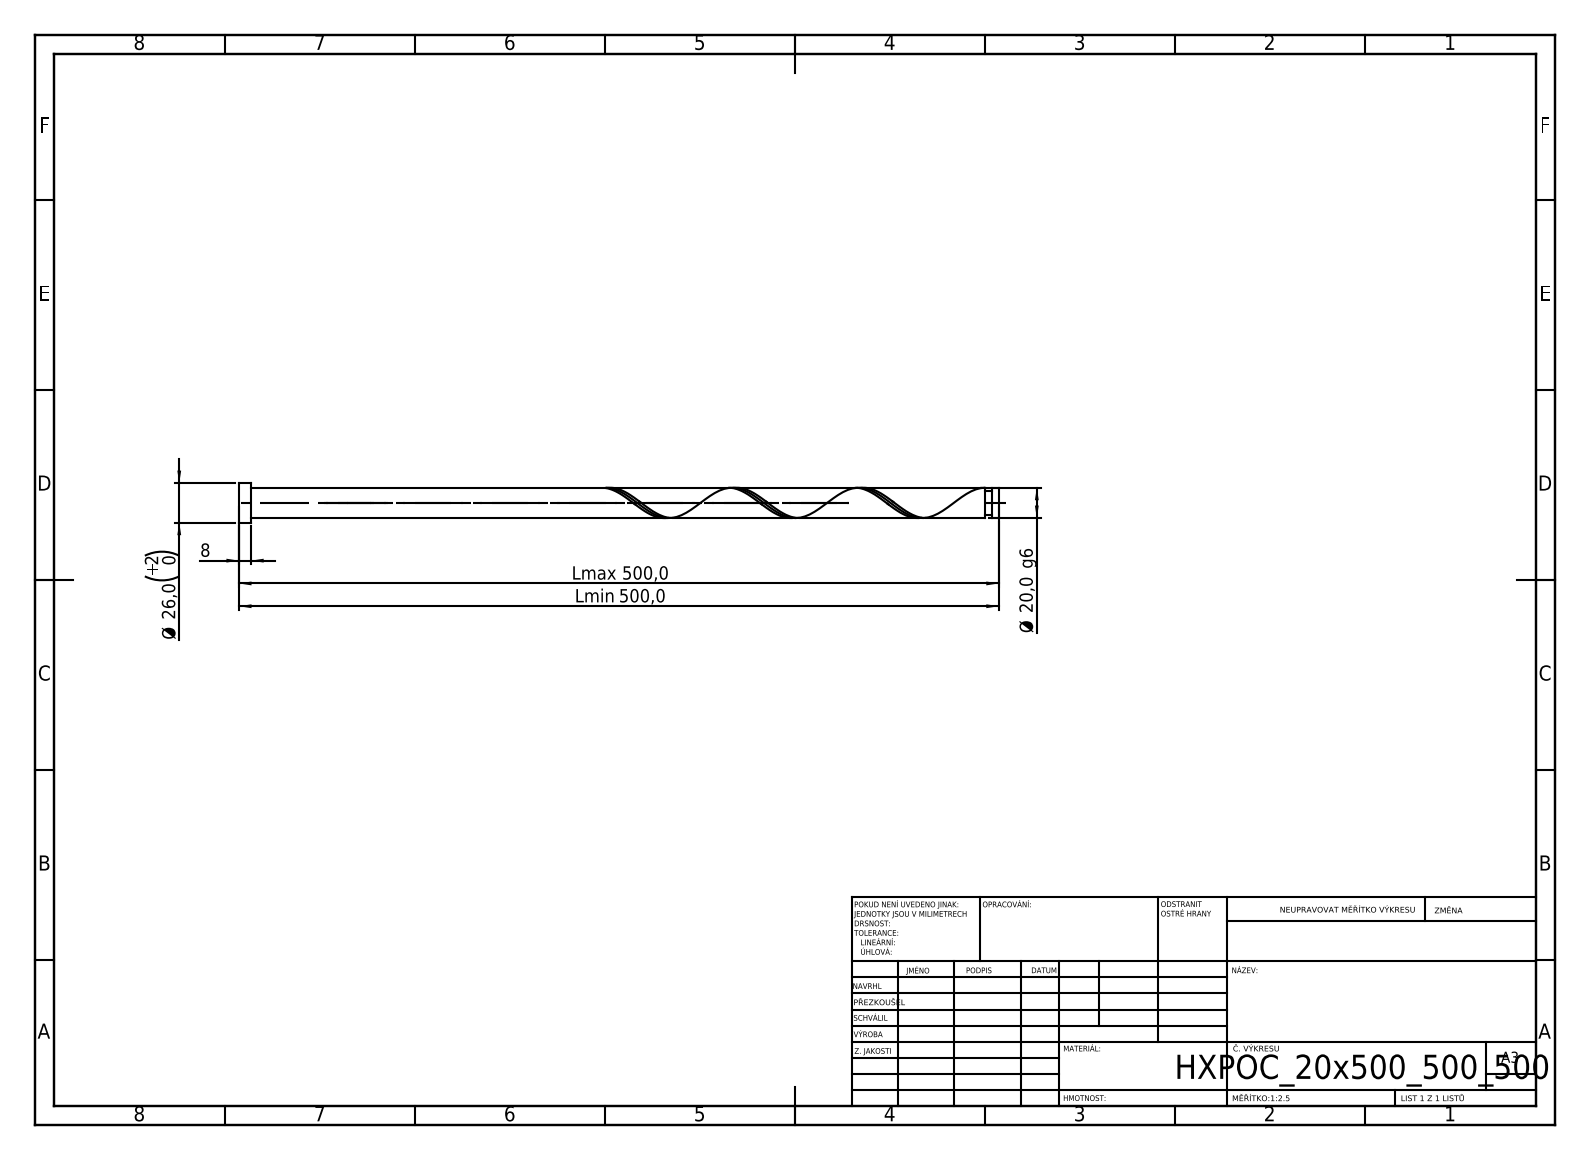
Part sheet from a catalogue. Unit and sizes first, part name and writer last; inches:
Units: inches
Overall size (bounding box): 19.685 × 1.024 × 1.024
Round bosses / shafts (diameter × count): ⌀1.024 ×1, ⌀0.787 ×1, ⌀0.63 ×1
Main face-to-face distances: 19.685, 0.315, 19.37, 19.495, 19.18, 0.19, 19.338, 19.023, 0.157, 0.347
Volume: 9.572 in³ · Surface area: 51.85 in²
Bodies: 1 solid, 21 faces (6 planar, 14 cylindrical, 1 other)
STEP written by: SolidWorks 2019 (CONFIG_CONTROL_DESIGN)
